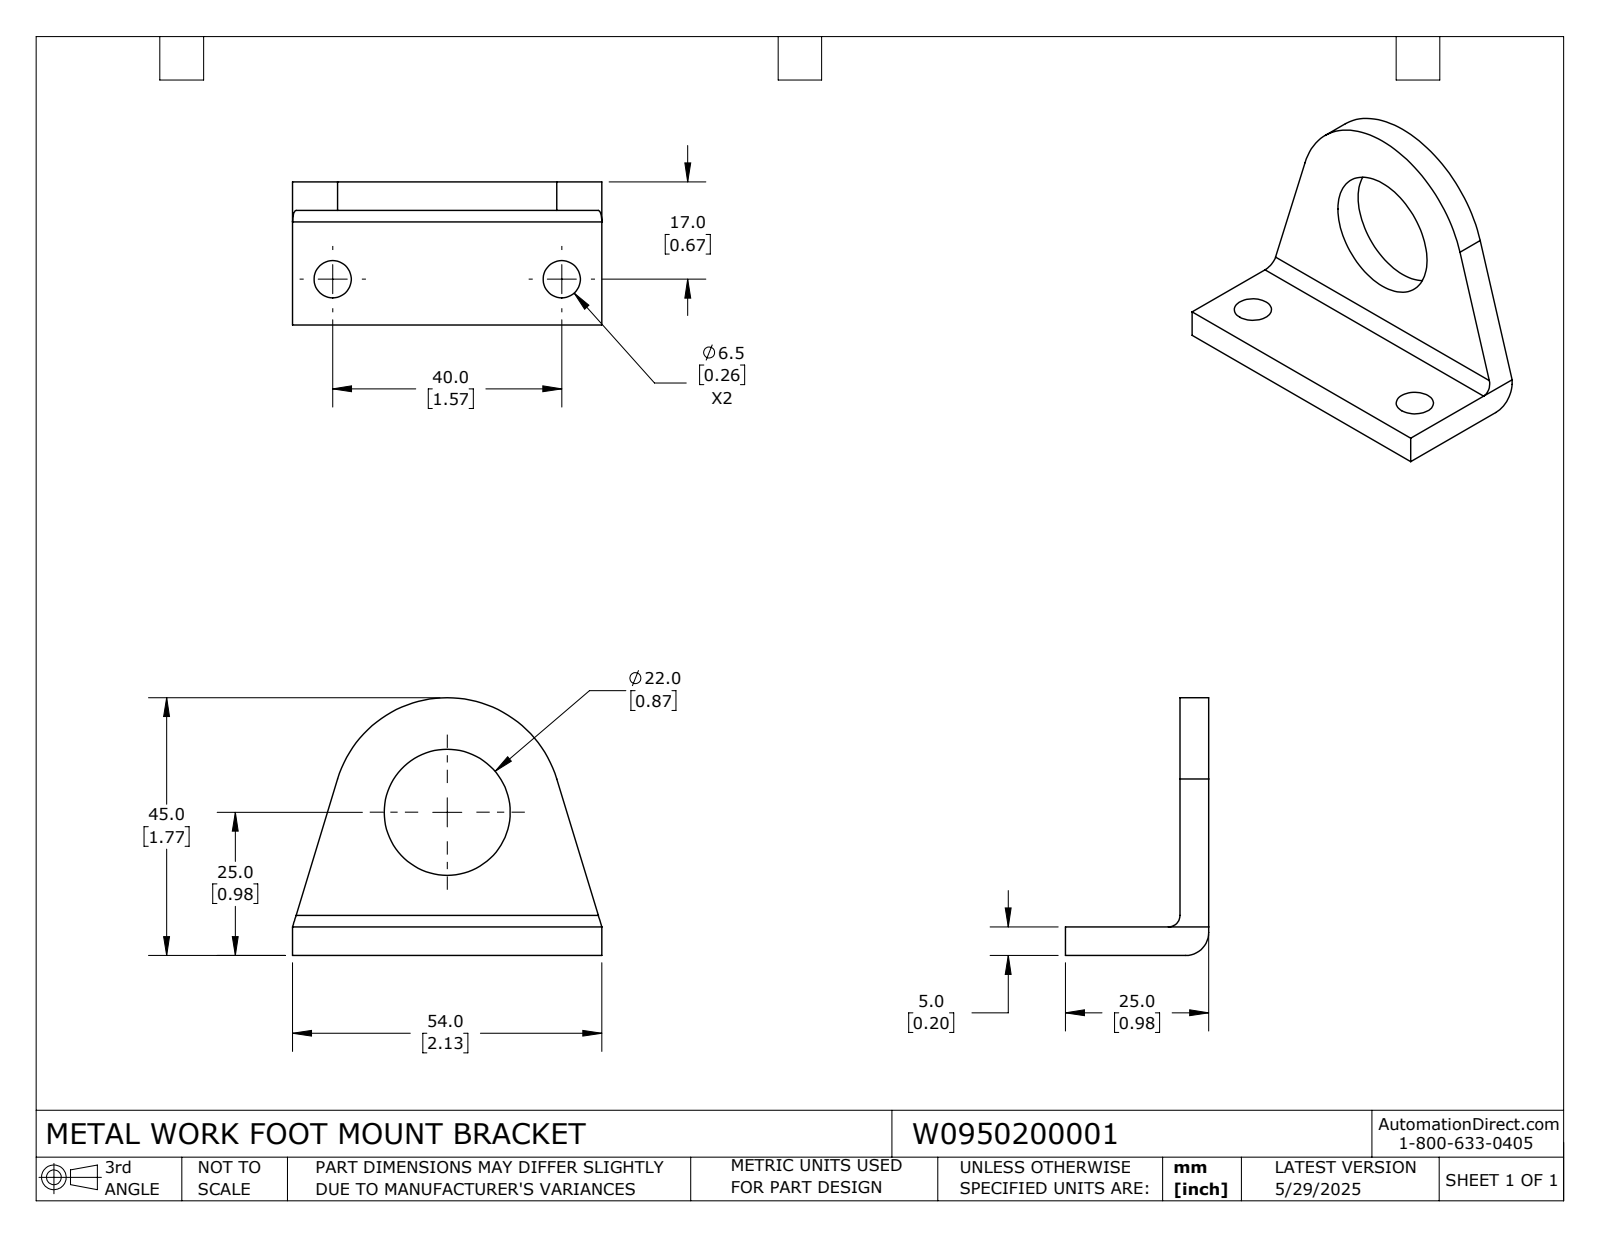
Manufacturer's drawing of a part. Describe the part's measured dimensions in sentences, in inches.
The part is named "W0950200001". Its 3-D file was written by "SolidWorks 2024 (CONFIG_CONTROL_DESIGN)". It is 1 solid with 18 faces: 9 planar, 9 cylindrical and 0 other. Overall it measures 2.126 by 1.772 by 0.984 inches. Its volume is 0.752 cubic inches and its surface area 9.978 square inches. Round holes: 2 of diameter 0.256, 1 of diameter 0.866. Partial cylindrical surfaces (rounded edges, fillets, slot ends): 1 of radius 0.079, 1 of radius 0.157, 1 of radius 0.787. The main face-to-face distances are 0.197, 0.984, 0.787, 2.126. The hole center spacings are 1.575.
